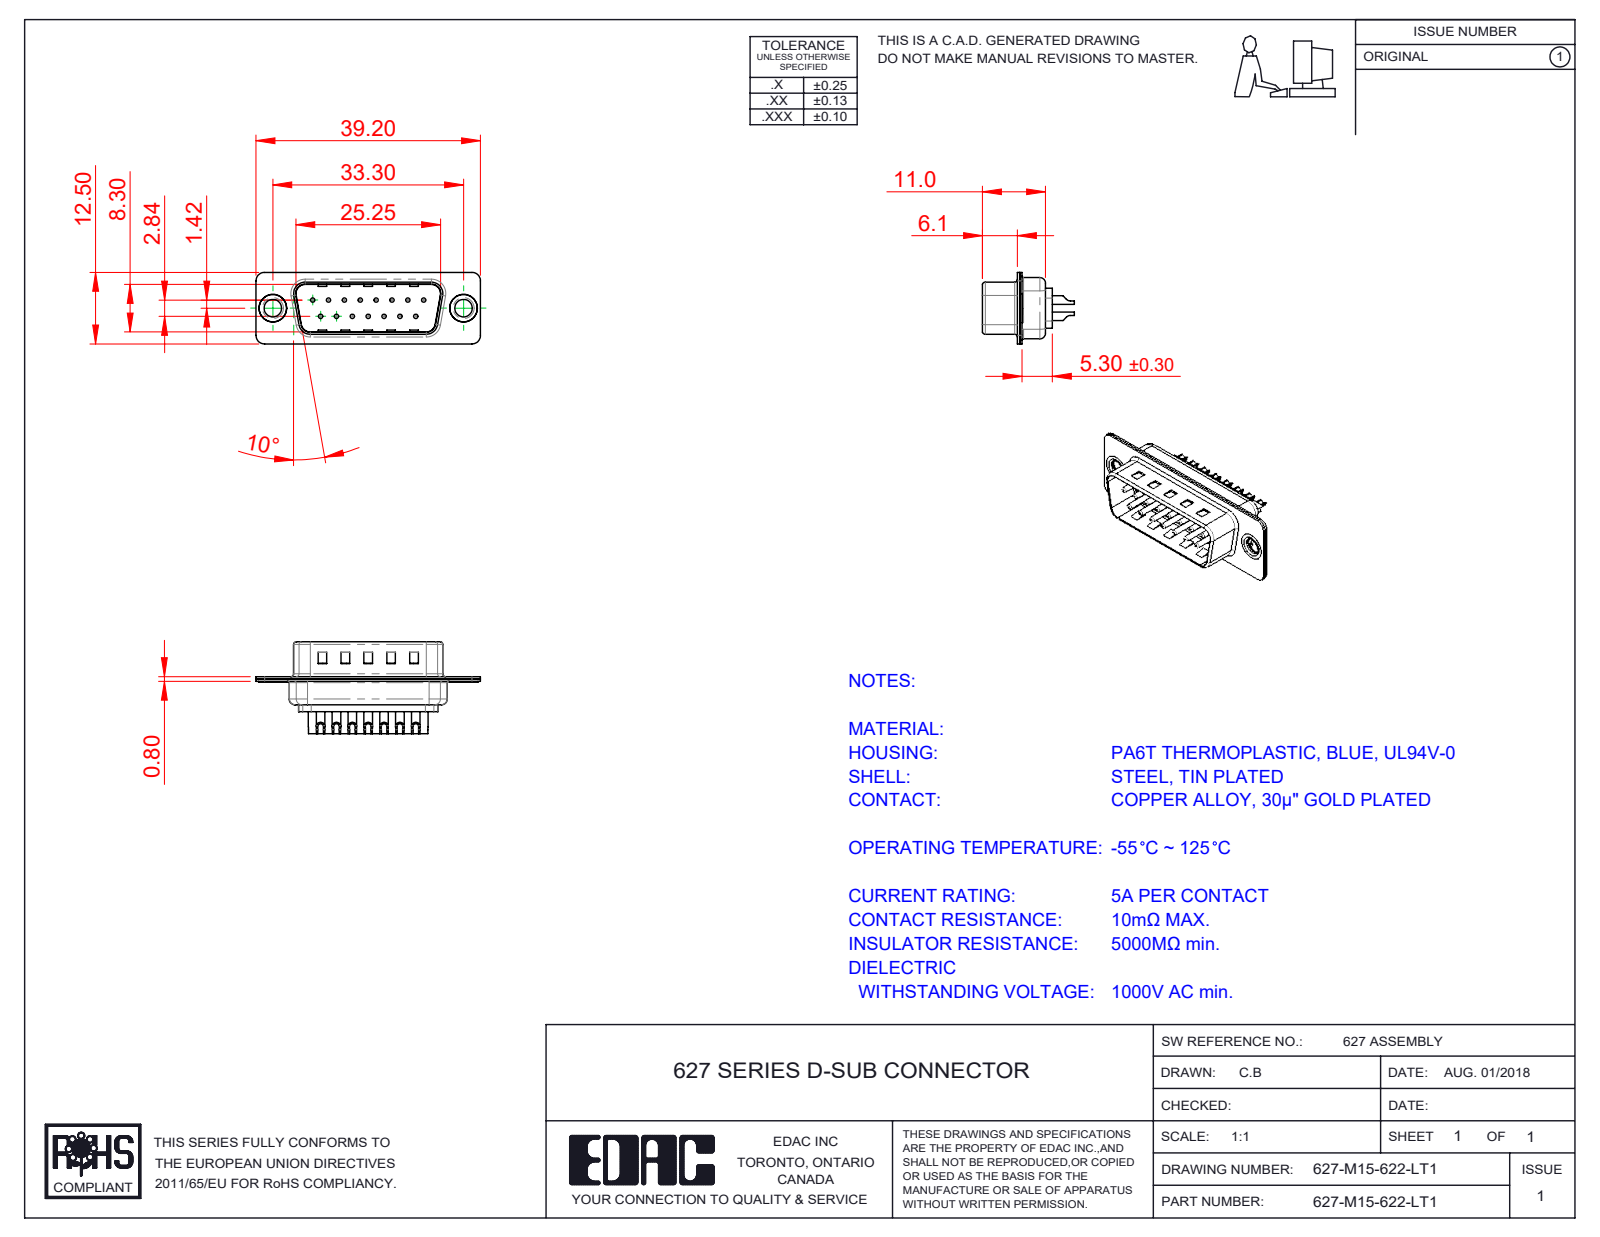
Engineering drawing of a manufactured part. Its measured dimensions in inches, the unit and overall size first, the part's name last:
Units: inches
Overall size (bounding box): 1.543 × 0.632 × 0.492
Round holes (diameter × count): ⌀0.03 ×15, ⌀0.039 ×15, ⌀0.063 ×15, ⌀0.079 ×15, ⌀0.12 ×2, ⌀0.157 ×2, ⌀0.189 ×2
Round bosses / shafts (diameter × count): ⌀0.059 ×15, ⌀0.197 ×2, ⌀0.193 ×2, ⌀0.14 ×2
Partial cylindrical surfaces — rounded edges, fillets, slot ends (radius × count): R0.059 ×16, R0.079 ×12, R0.02 ×8, R0.063 ×8, R0.039 ×6, R0.01 ×4, R0.024 ×4, R0.026 ×4
Main face-to-face distances: 0.016, 0.031, 0.374, 0.358, 0.343, 0.39, 0.047, 0.03, 0.014, 0.24
Hole centre spacings: 0.124, 0.109, 0.218, 0.327, 0.436, 0.198, 0.198, 0.294
Volume: 0.11 in³ · Surface area: 7.446 in²
Bodies: 20 solids, 869 faces (274 planar, 357 cylindrical, 238 other)
Part name (STEP PRODUCT): 627M Housing_15 Contacts; 627M Shell Front_15 Contacts; 627M Shell Rear_15 Contacts; 627M Thru Hole Rivet (+3 more)
STEP written by: SolidWorks 2020 (CONFIG_CONTROL_DESIGN)
